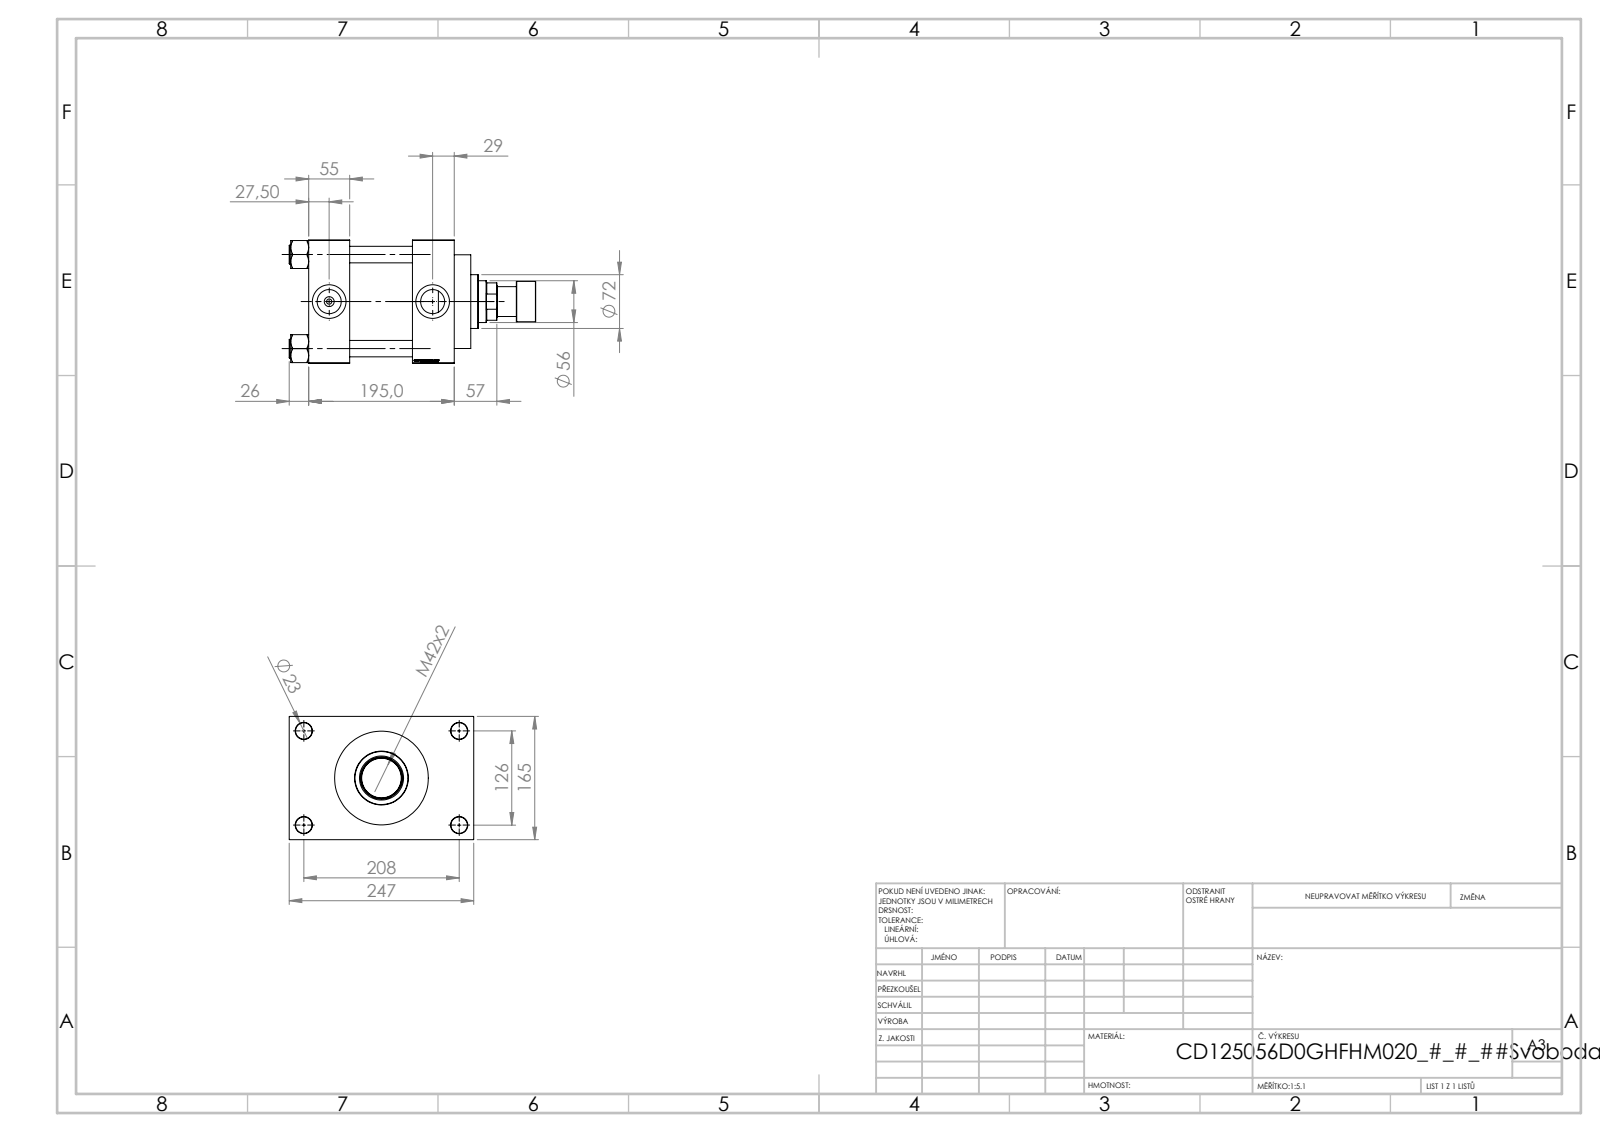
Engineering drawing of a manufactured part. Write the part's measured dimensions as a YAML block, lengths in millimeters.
part_name: "V215CR_ROD_END_F; V215CD_VC_A; V215CD_VCP_D; V215CD_D_TYCINKA (+2 more)"
step_written_by: "SolidWorks 2019 (CONFIG_CONTROL_DESIGN)"
units: millimeters
bodies: {solids: 12, faces: 1162, planar: 548, cylindrical: 90, other: 524}
overall_size: [330, 247, 165]
volume: 5017000
surface_area: 546598
round_holes:
  - {diameter: 22, count: 8}
  - {diameter: 7, count: 2}
  - {diameter: 32.24, count: 2}
  - {diameter: 45, count: 2}
  - {diameter: 40.5, count: 1}
  - {diameter: 56, count: 1}
  - {diameter: 59, count: 1}
  - {diameter: 96, count: 1}
  - {diameter: 125, count: 1}
  - {diameter: 125.5, count: 1}
round_bosses_or_shafts:
  - {diameter: 25, count: 4}
  - {diameter: 131, count: 1}
  - {diameter: 72, count: 1}
  - {diameter: 54, count: 1}
  - {diameter: 40, count: 1}
face_to_face_distances: [165, 139, 84, 55, 56, 195, 140, 41, 206, 173.74]
hole_center_spacings: [41.05, 89.02, 121.59, 125.9, 132.47, 166.95, 209.13, 126]
